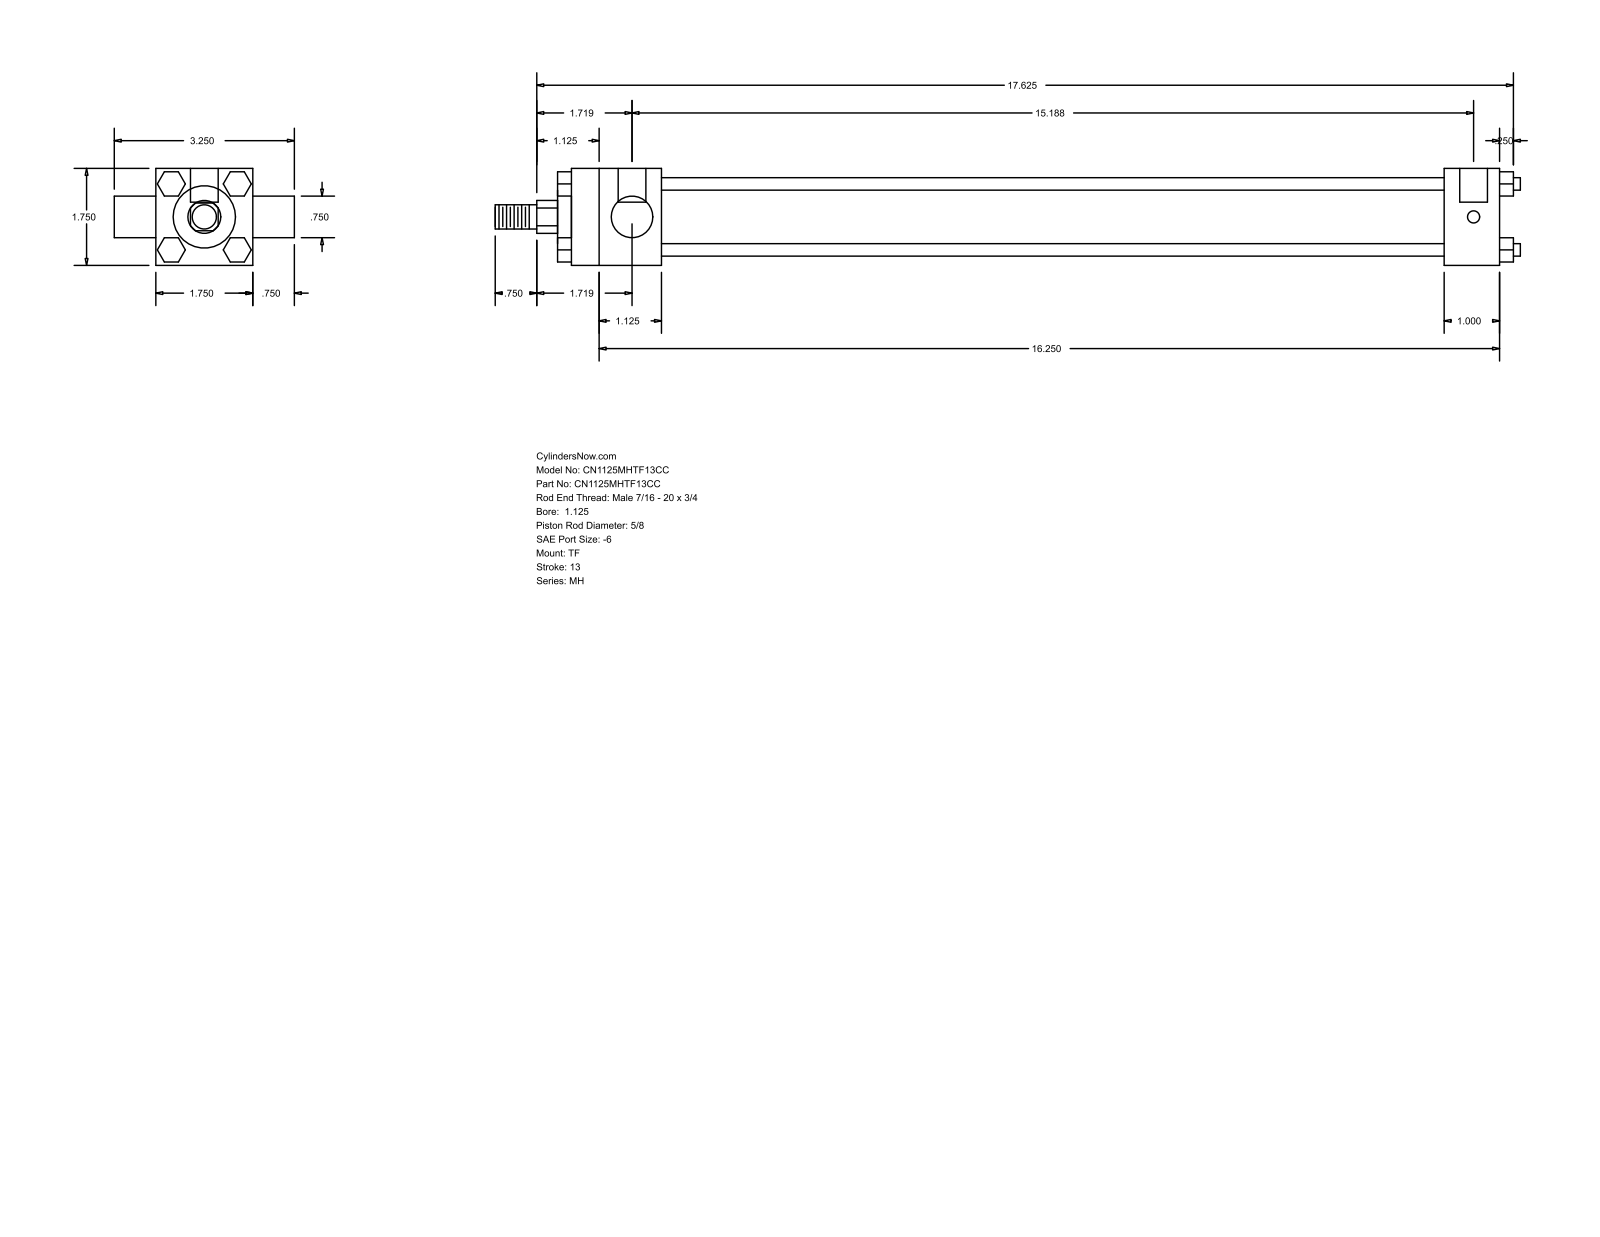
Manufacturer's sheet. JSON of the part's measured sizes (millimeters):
{"part_name": "MH_TF__0112_0.625", "step_written_by": "GSSL Pune (CONFIG_CONTROL_DESIGN)", "units": "millimeters", "bodies": {"solids": 0, "faces": 120, "planar": 92, "cylindrical": 28, "other": 0}, "overall_size": [469.9, 82.55, 44.45], "round_holes": [[5.56, 3], [12.7, 2]], "round_bosses_or_shafts": [[5.71, 4], [34.92, 1], [28.57, 1], [19.05, 1], [15.88, 1], [11.11, 1]], "partial_cylinders_radius": [[7.54, 1]], "face_to_face_distances": [44.46, 11.11, 358.78, 384.17, 25.39, 41.27, 400.05, 425.44, 47.62, 6.35], "hole_center_spacings": [3.17, 382.59, 385.76]}
